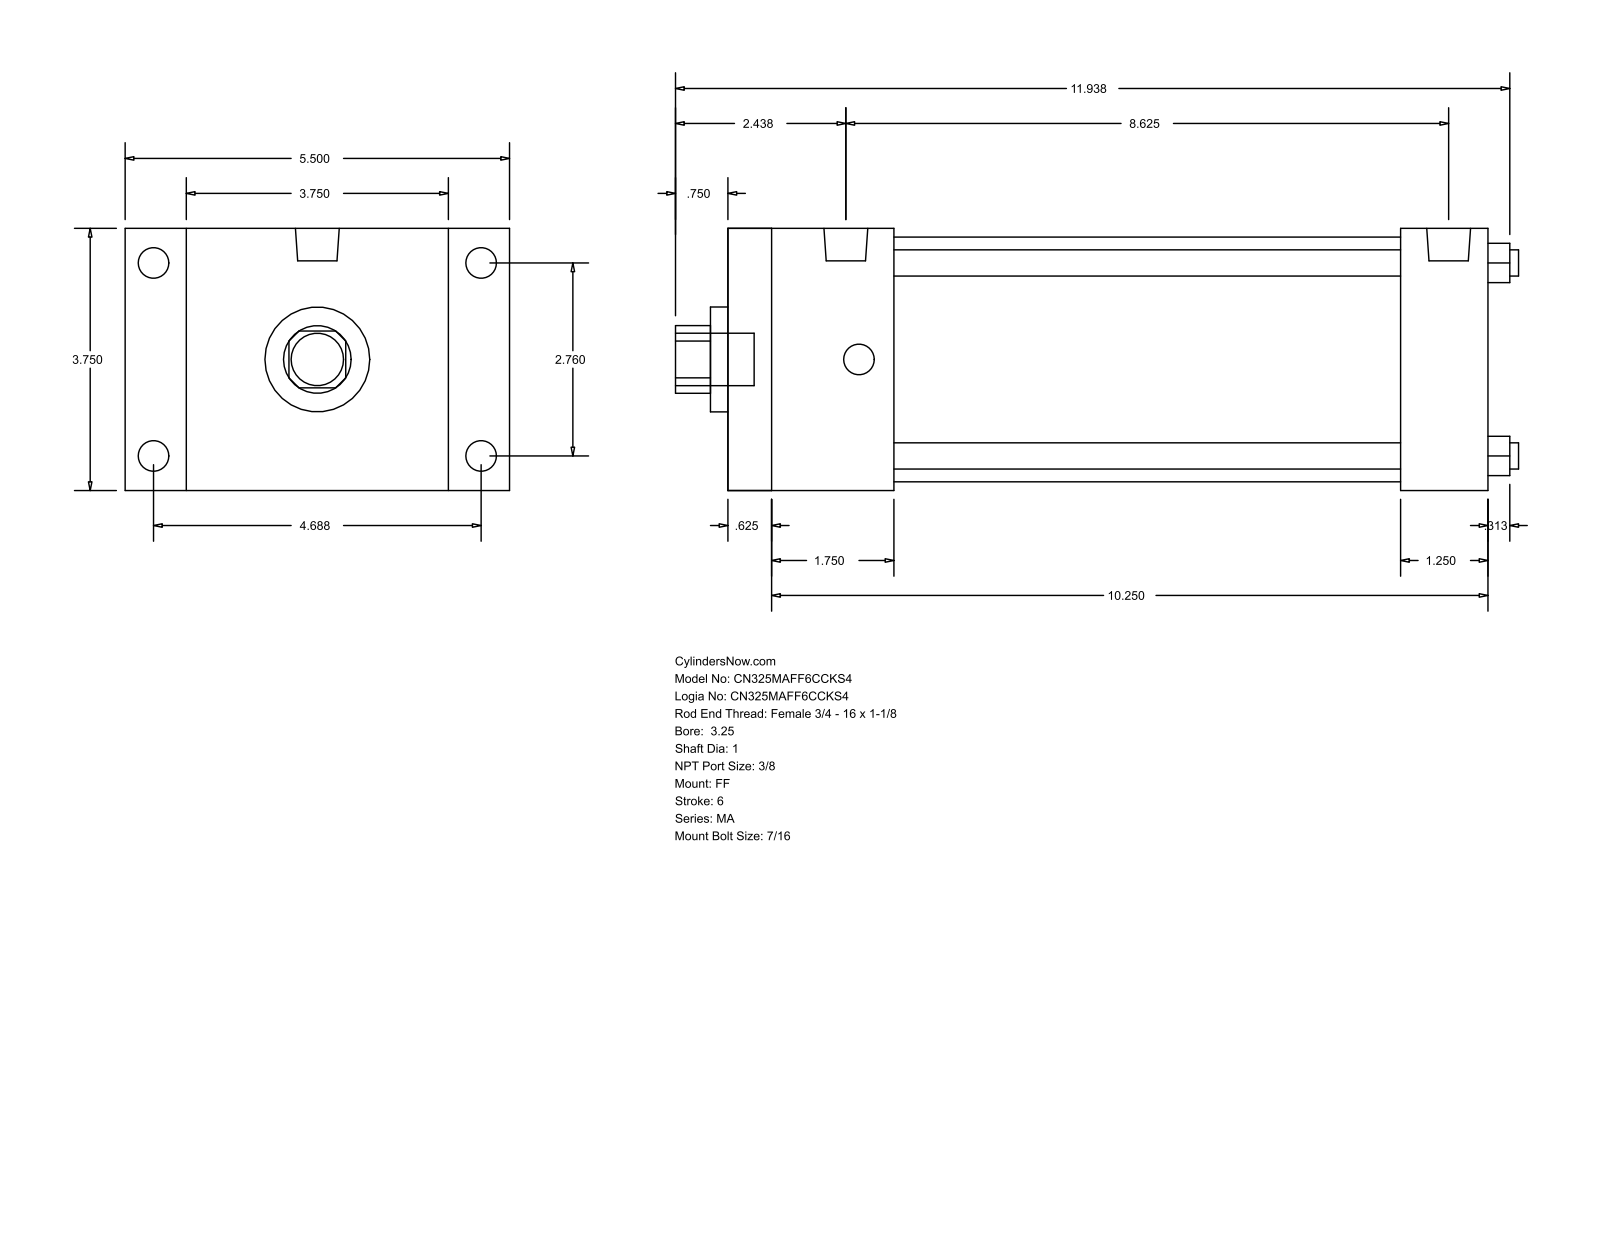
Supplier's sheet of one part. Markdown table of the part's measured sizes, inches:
| quantity | value |
| --- | --- |
| part name | MA_FF__0325_1 |
| STEP written by | GSSL Pune (CONFIG_CONTROL_DESIGN) |
| units | inches |
| bodies | 0 solids, 92 faces (64 planar, 28 cylindrical, 0 other) |
| overall size | 12.063 × 5.5 × 3.75 |
| round holes (diameter × count) | 0.375 × 4, 1 × 1, 1.5 × 1, 3.5 × 1 |
| round bosses / shafts (diameter × count) | 0.437 × 8, 0.627 × 2, 0.75 × 1 |
| partial cylindrical surfaces (radius × count) | 0.484 × 1 |
| main face-to-face distances | 3.75, 10.875, 0.625, 10.25, 0.875, 4.625, 2.375, 9.625, 1.75, 9 |
| hole center spacings | 1.952, 2.76, 3.903 |
